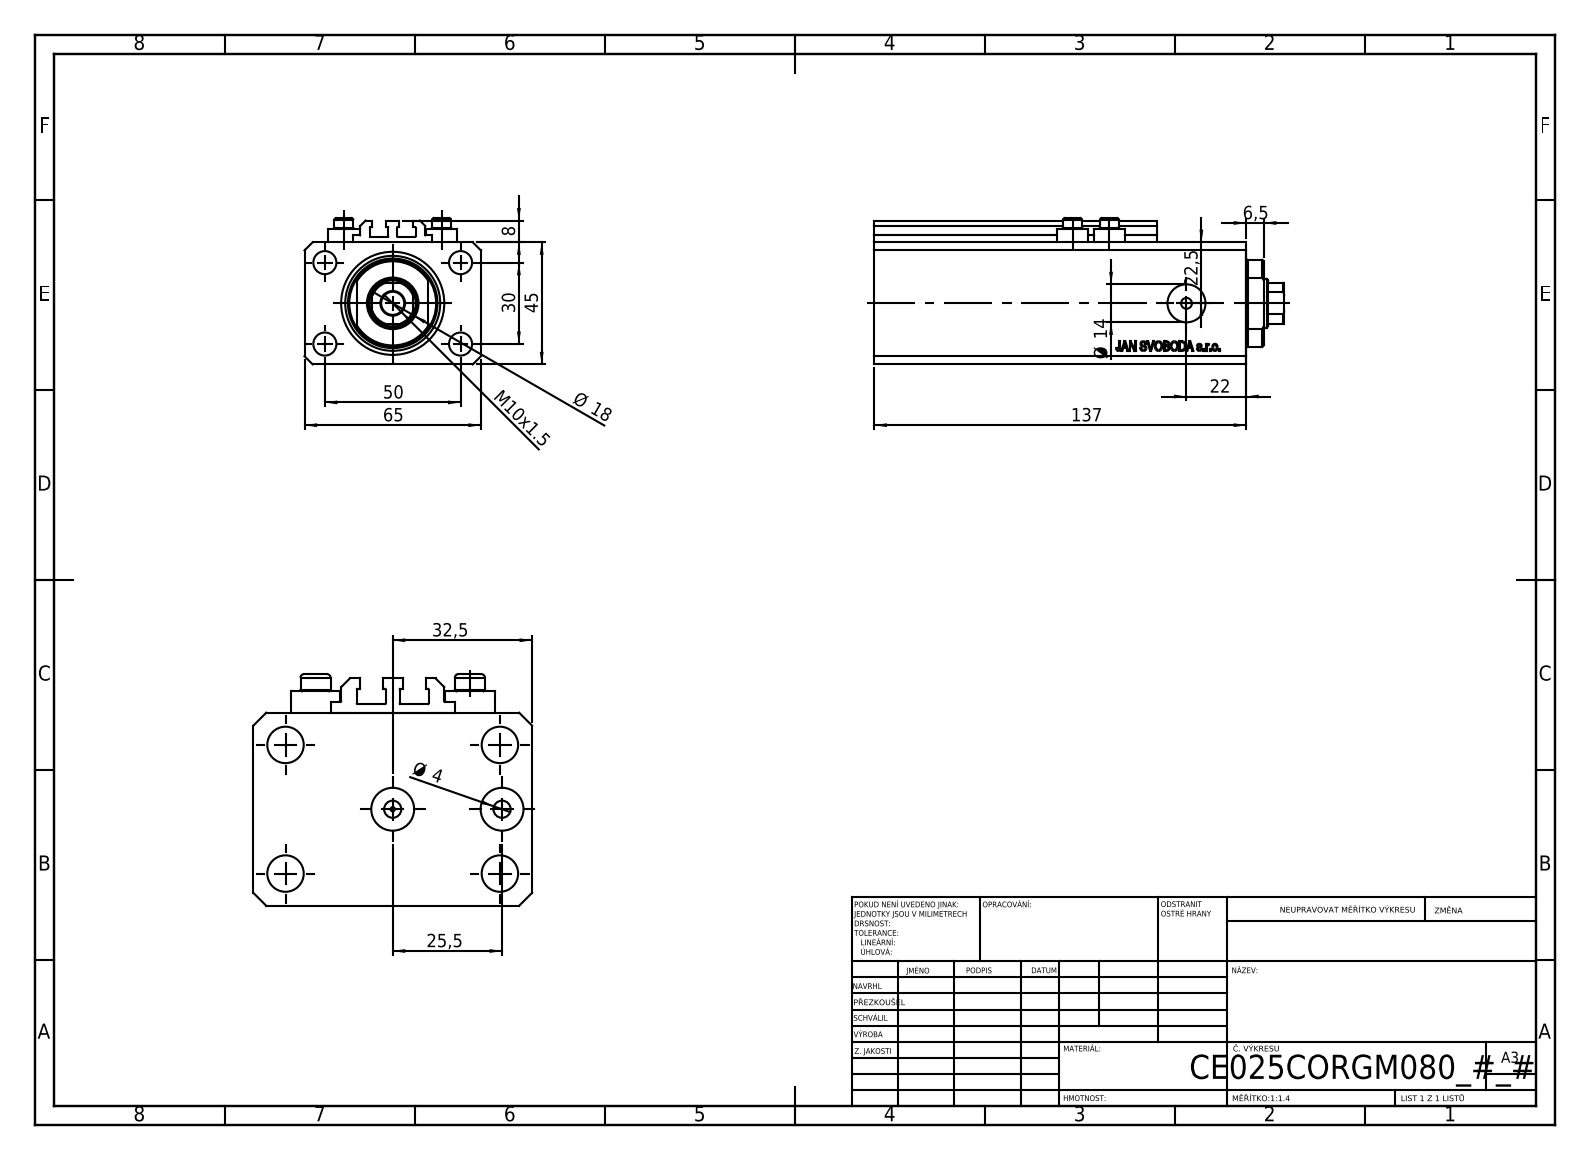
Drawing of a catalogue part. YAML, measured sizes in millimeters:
part_name: "V250CE_C_Body; V250CE_VC_C; ALLEN BOLT V250CE; V250CE_C_VCP"
step_written_by: "SolidWorks 2019 (CONFIG_CONTROL_DESIGN)"
units: millimeters
bodies: {solids: 8, faces: 1038, planar: 504, cylindrical: 88, other: 446}
overall_size: [151, 65, 54]
volume: 365646
surface_area: 91085
round_holes:
  - {diameter: 4, count: 8}
  - {diameter: 8.5, count: 5}
  - {diameter: 10, count: 2}
  - {diameter: 14, count: 2}
  - {diameter: 1.25, count: 1}
  - {diameter: 18, count: 1}
  - {diameter: 25, count: 1}
  - {diameter: 38, count: 1}
round_bosses_or_shafts:
  - {diameter: 11.6, count: 4}
  - {diameter: 7, count: 4}
partial_cylinders:
  - {radius: 0.2, count: 10}
  - {radius: 8.5, count: 1}
  - {radius: 16, count: 1}
face_to_face_distances: [45, 65, 47, 14, 137, 123, 2.5, 2, 10, 20.5]
hole_center_spacings: [29.15, 13.6, 15.01, 30, 36, 38.48, 50, 52.68]
